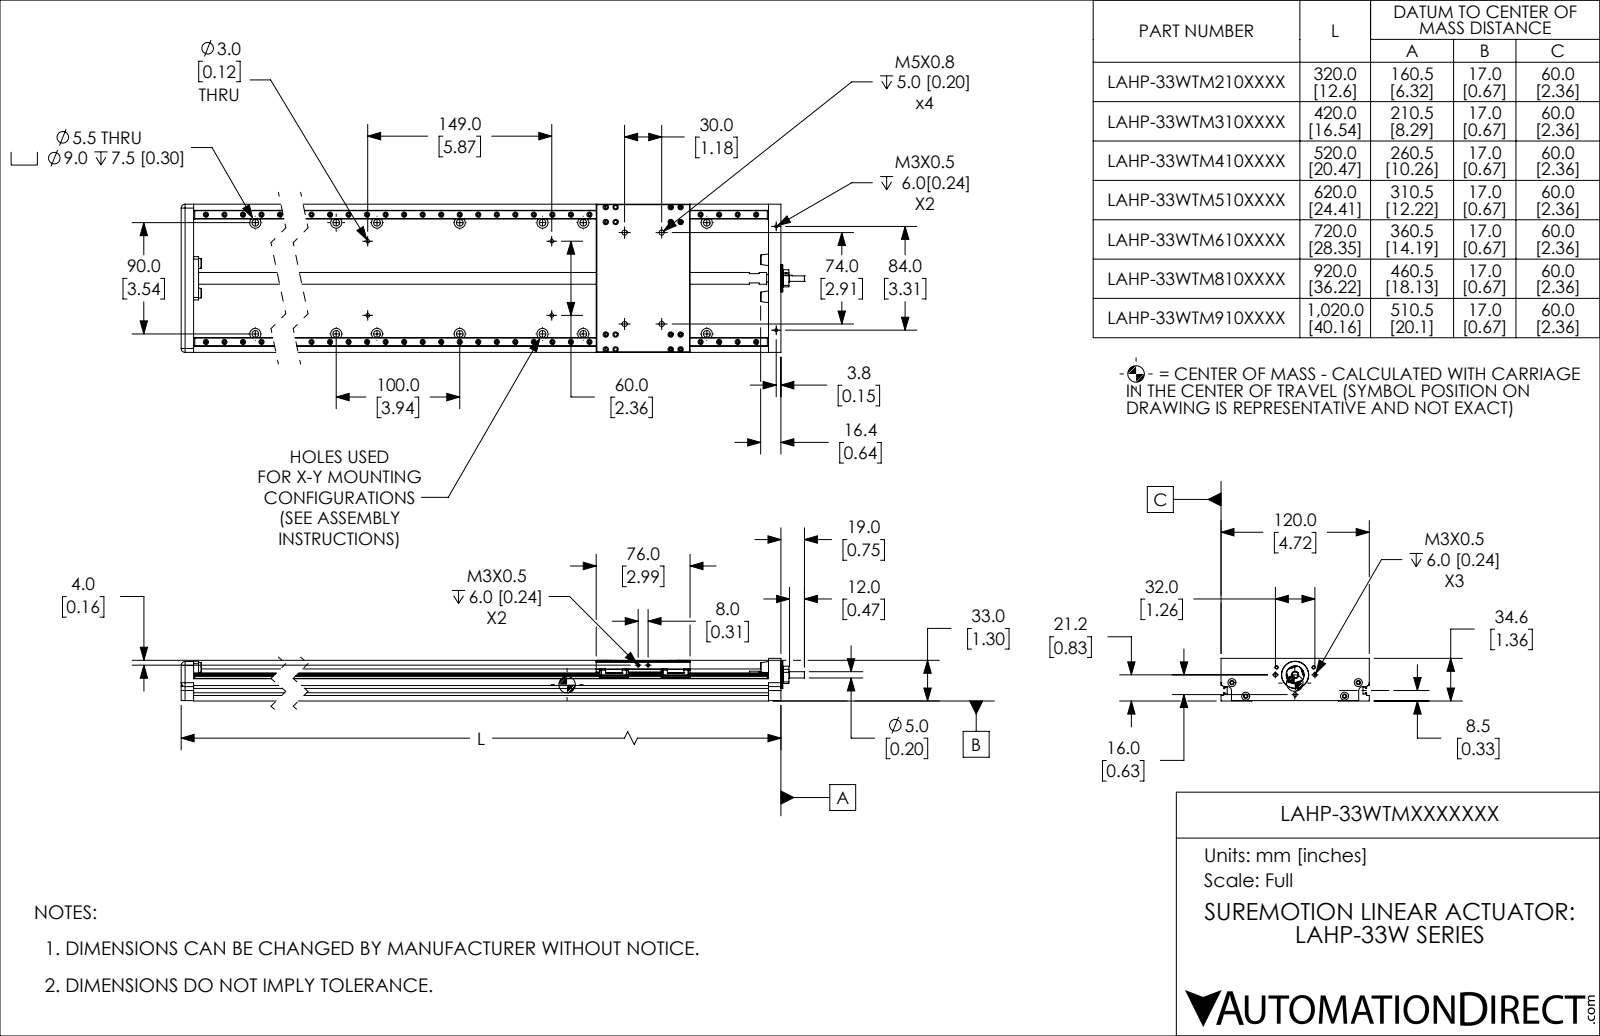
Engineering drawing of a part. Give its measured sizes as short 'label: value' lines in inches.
name: LAHP-33WTM910B10M; LAHP-33WTM910B10M_CARRIAGE; LAHP-33WTM910B10M_BASE
written by: SolidWorks 2019 (CONFIG_CONTROL_DESIGN)
unit: in
bodies: 2 solids, 2497 faces (791 planar, 1290 cylindrical, 416 other)
size: 40.908 × 4.724 × 1.362
volume: 87.92 in³; area: 705.2 in²
holes: 138× ⌀0.165, 136× ⌀0.063, 134× ⌀0.094, 24× ⌀0.217, 24× ⌀0.354, 16× ⌀0.062, 16× ⌀0.102, 16× ⌀0.173, 14× ⌀0.098, 10× ⌀0.118, 4× ⌀0.094, 4× ⌀0.13
bosses: 1× ⌀0.866, 1× ⌀0.748, 1× ⌀0.61, 1× ⌀0.571, 1× ⌀0.528, 1× ⌀0.409, 1× ⌀0.394, 1× ⌀0.375
rounds: 16× R0.125, 8× R0.006, 8× R0.02, 4× R0.034, 2× R0.012
face distances: 0.279, 0.309, 0.03, 0.472, 4.252, 0.276, 4.055, 0.197, 4.528, 0.354
hole spacings: 3.937, 5.297, 7.874, 8.635, 11.811, 12.331, 3.543, 15.748
